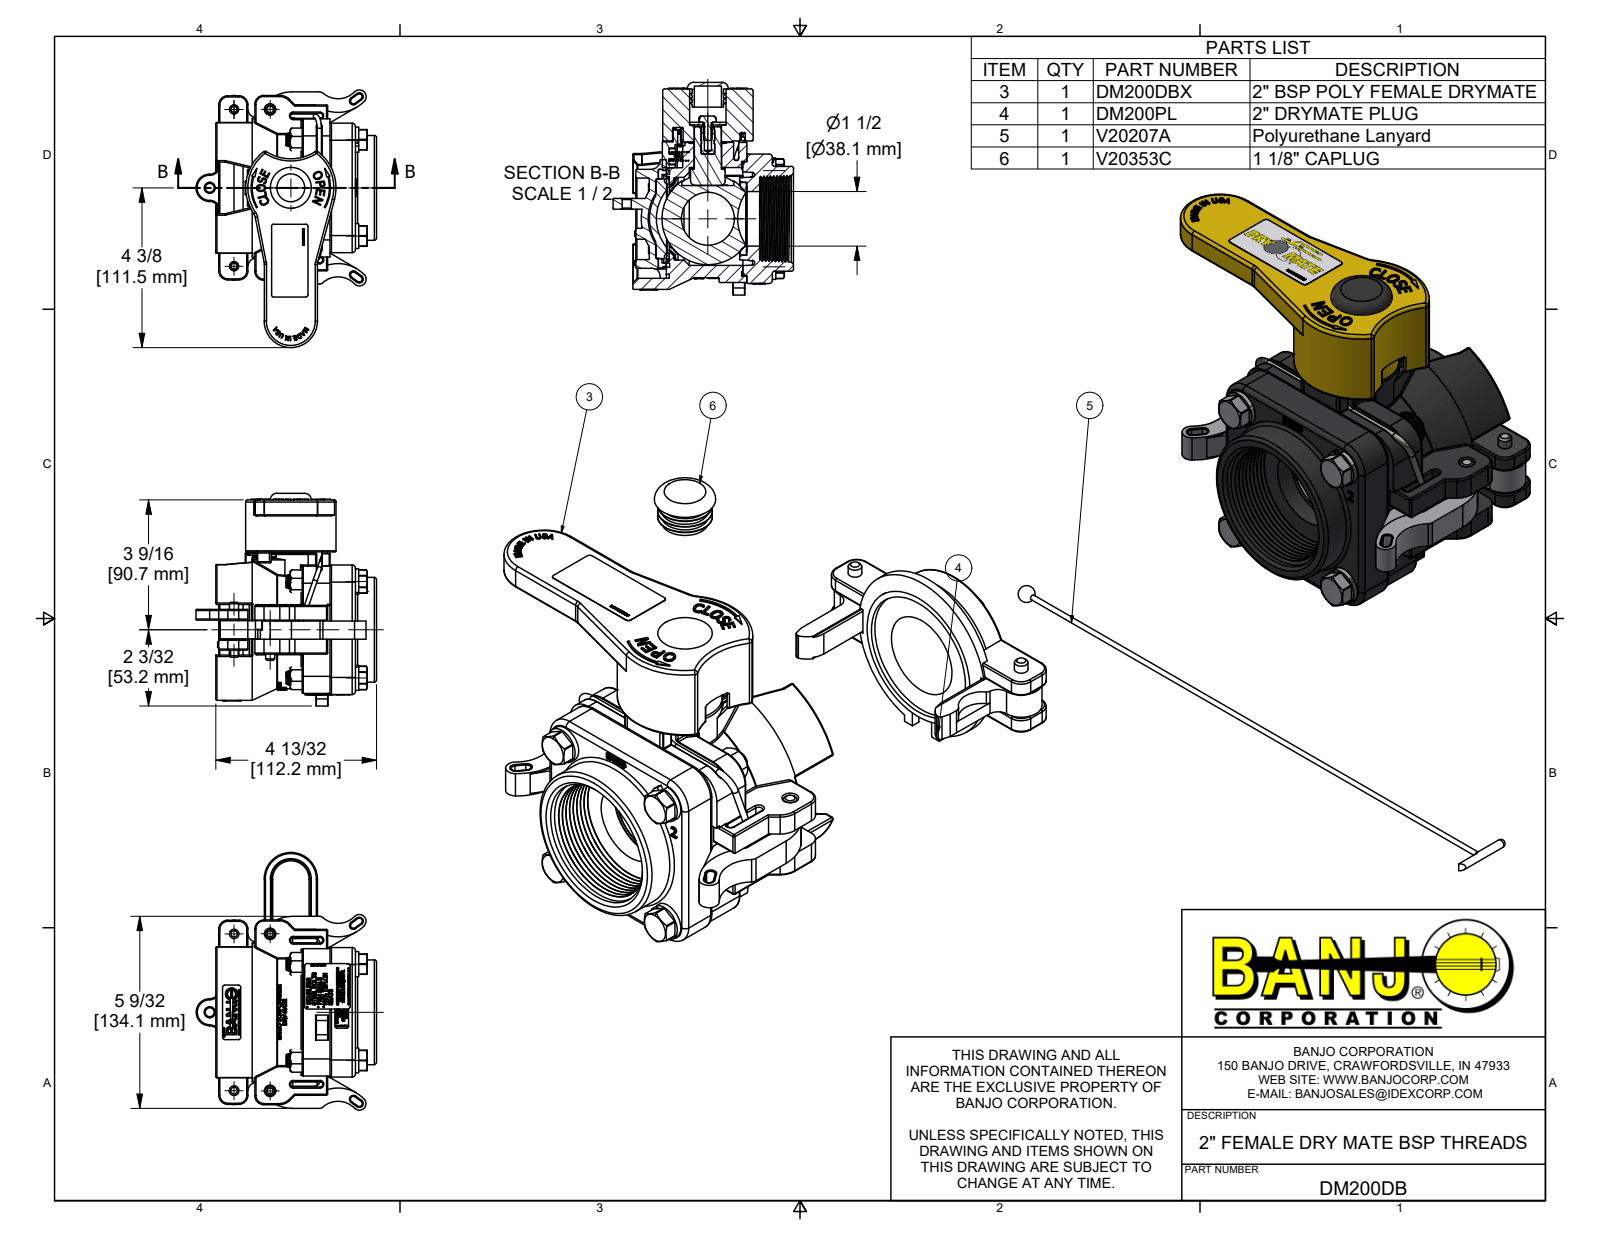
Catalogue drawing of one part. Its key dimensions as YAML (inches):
part_name: "DM200DB; DM200DBX; DM20254F; DM20254FY (+8 more)"
step_written_by: "Autodesk Inventor 2022 (AUTOMOTIVE_DESIGN)"
units: inches
bodies: {solids: 41, faces: 4341, planar: 1685, cylindrical: 995, other: 1661}
overall_size: [7.084, 5.685, 4.962]
volume: 45.07
surface_area: 389.1
round_holes:
  - {diameter: 0.25, count: 5}
  - {diameter: 0.375, count: 5}
  - {diameter: 0.256, count: 4}
  - {diameter: 0.307, count: 4}
  - {diameter: 0.385, count: 4}
  - {diameter: 0.406, count: 4}
  - {diameter: 0.41, count: 4}
  - {diameter: 0.125, count: 3}
  - {diameter: 0.196, count: 1}
  - {diameter: 0.2, count: 1}
  - {diameter: 0.281, count: 1}
  - {diameter: 0.351, count: 1}
round_bosses_or_shafts:
  - {diameter: 0.324, count: 60}
  - {diameter: 0.12, count: 5}
  - {diameter: 0.687, count: 4}
  - {diameter: 0.375, count: 4}
  - {diameter: 0.26, count: 4}
  - {diameter: 0.249, count: 4}
  - {diameter: 0.28, count: 3}
  - {diameter: 3.25, count: 1}
partial_cylinders:
  - {radius: 0.03, count: 159}
  - {radius: 0.01, count: 41}
  - {radius: 0.06, count: 31}
  - {radius: 0.02, count: 20}
  - {radius: 0.25, count: 11}
  - {radius: 0.12, count: 10}
  - {radius: 0.08, count: 8}
  - {radius: 0.09, count: 8}
face_to_face_distances: [0.92, 0.298, 0.11, 0.7, 0.013, 2.217, 0.5, 0.08, 3.833, 3.137]
hole_center_spacings: [2.654, 1.872, 1.881, 2.648, 2.66, 3.753, 0.95, 0.986]
